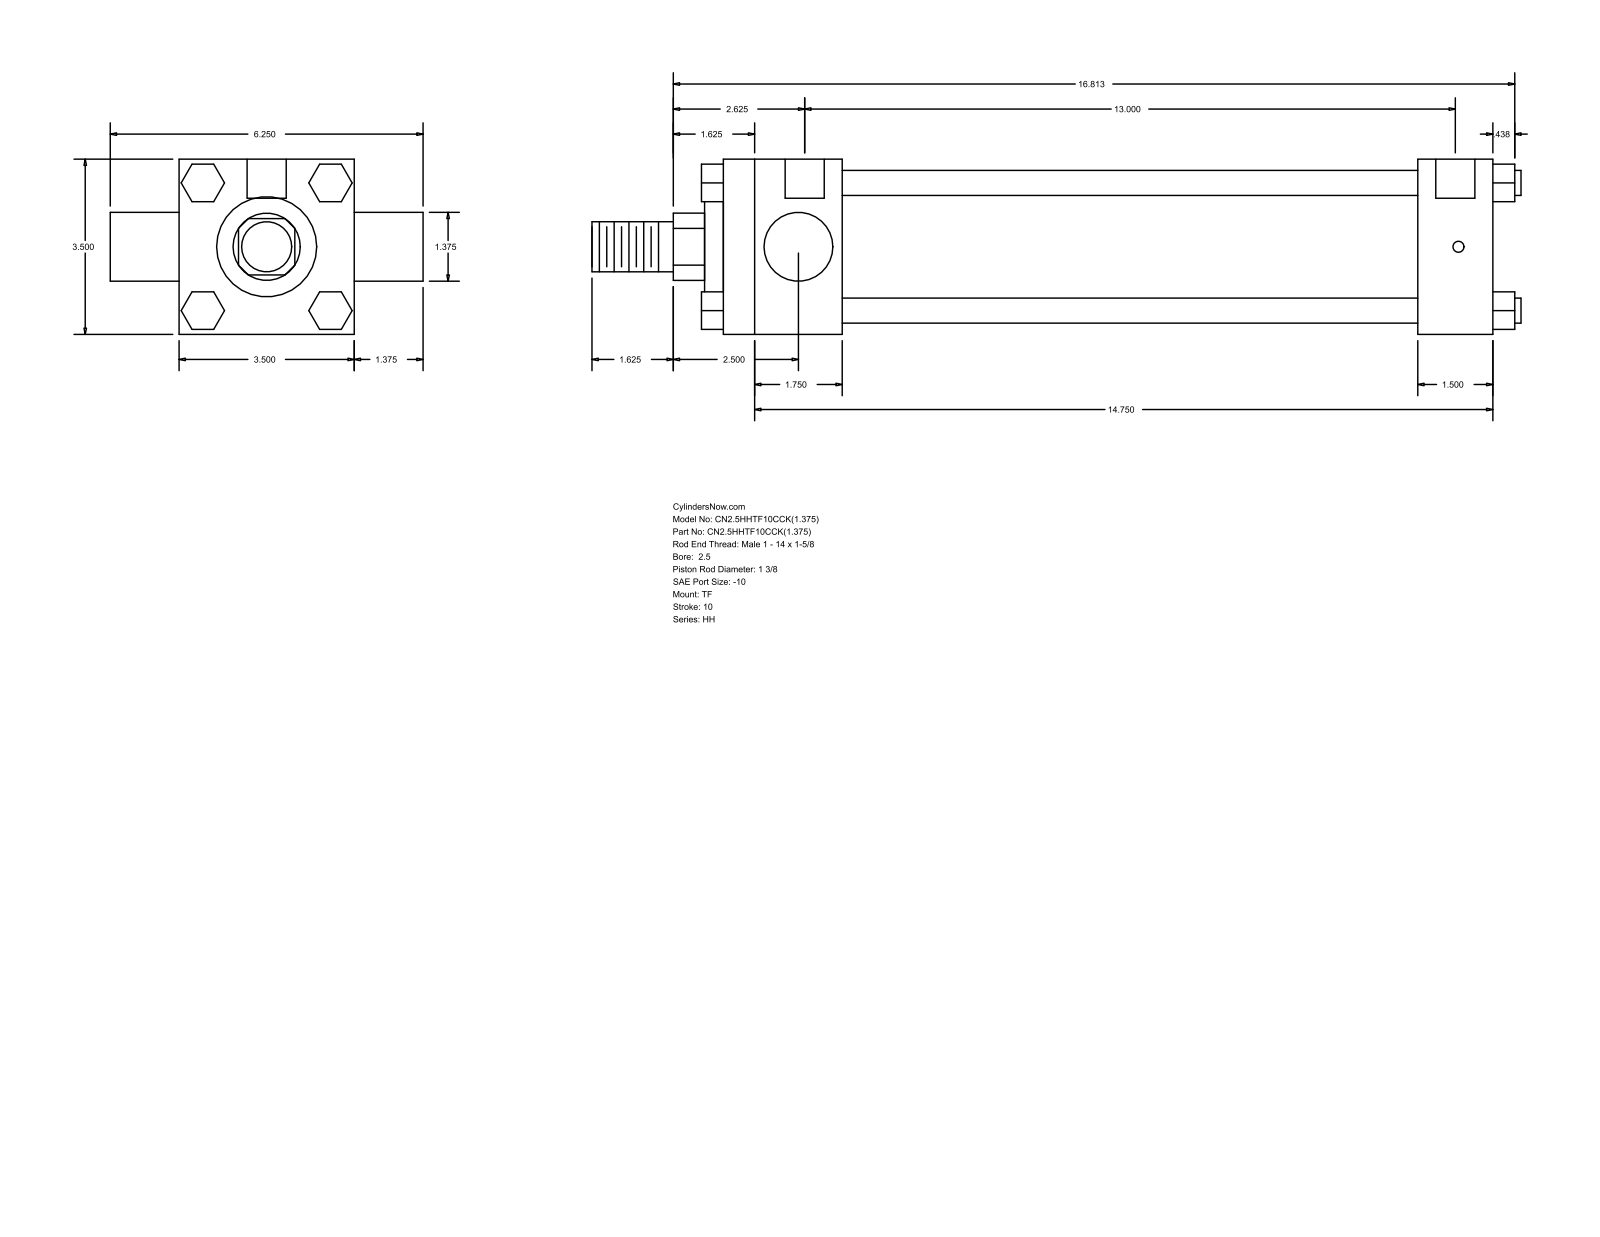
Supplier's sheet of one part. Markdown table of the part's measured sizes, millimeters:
| quantity | value |
| --- | --- |
| part name | HH_TF__0250_1.375 |
| STEP written by | GSSL Pune (CONFIG_CONTROL_DESIGN) |
| units | millimeters |
| bodies | 0 solids, 120 faces (92 planar, 28 cylindrical, 0 other) |
| overall size | 471.49 × 158.75 × 88.9 |
| round holes (diameter × count) | 5.56 × 3, 19.84 × 2 |
| round bosses / shafts (diameter × count) | 12.7 × 4, 34.92 × 2, 73.03 × 1, 50.8 × 1, 25.4 × 1 |
| partial cylindrical surfaces (radius × count) | 17.06 × 1 |
| main face-to-face distances | 88.9, 390.53, 60.32, 330.21, 352.42, 292.1, 38.11, 19.05, 32.38, 56.09 |
| hole center spacings | 1.58, 331.79, 330.21, 333.37 |
